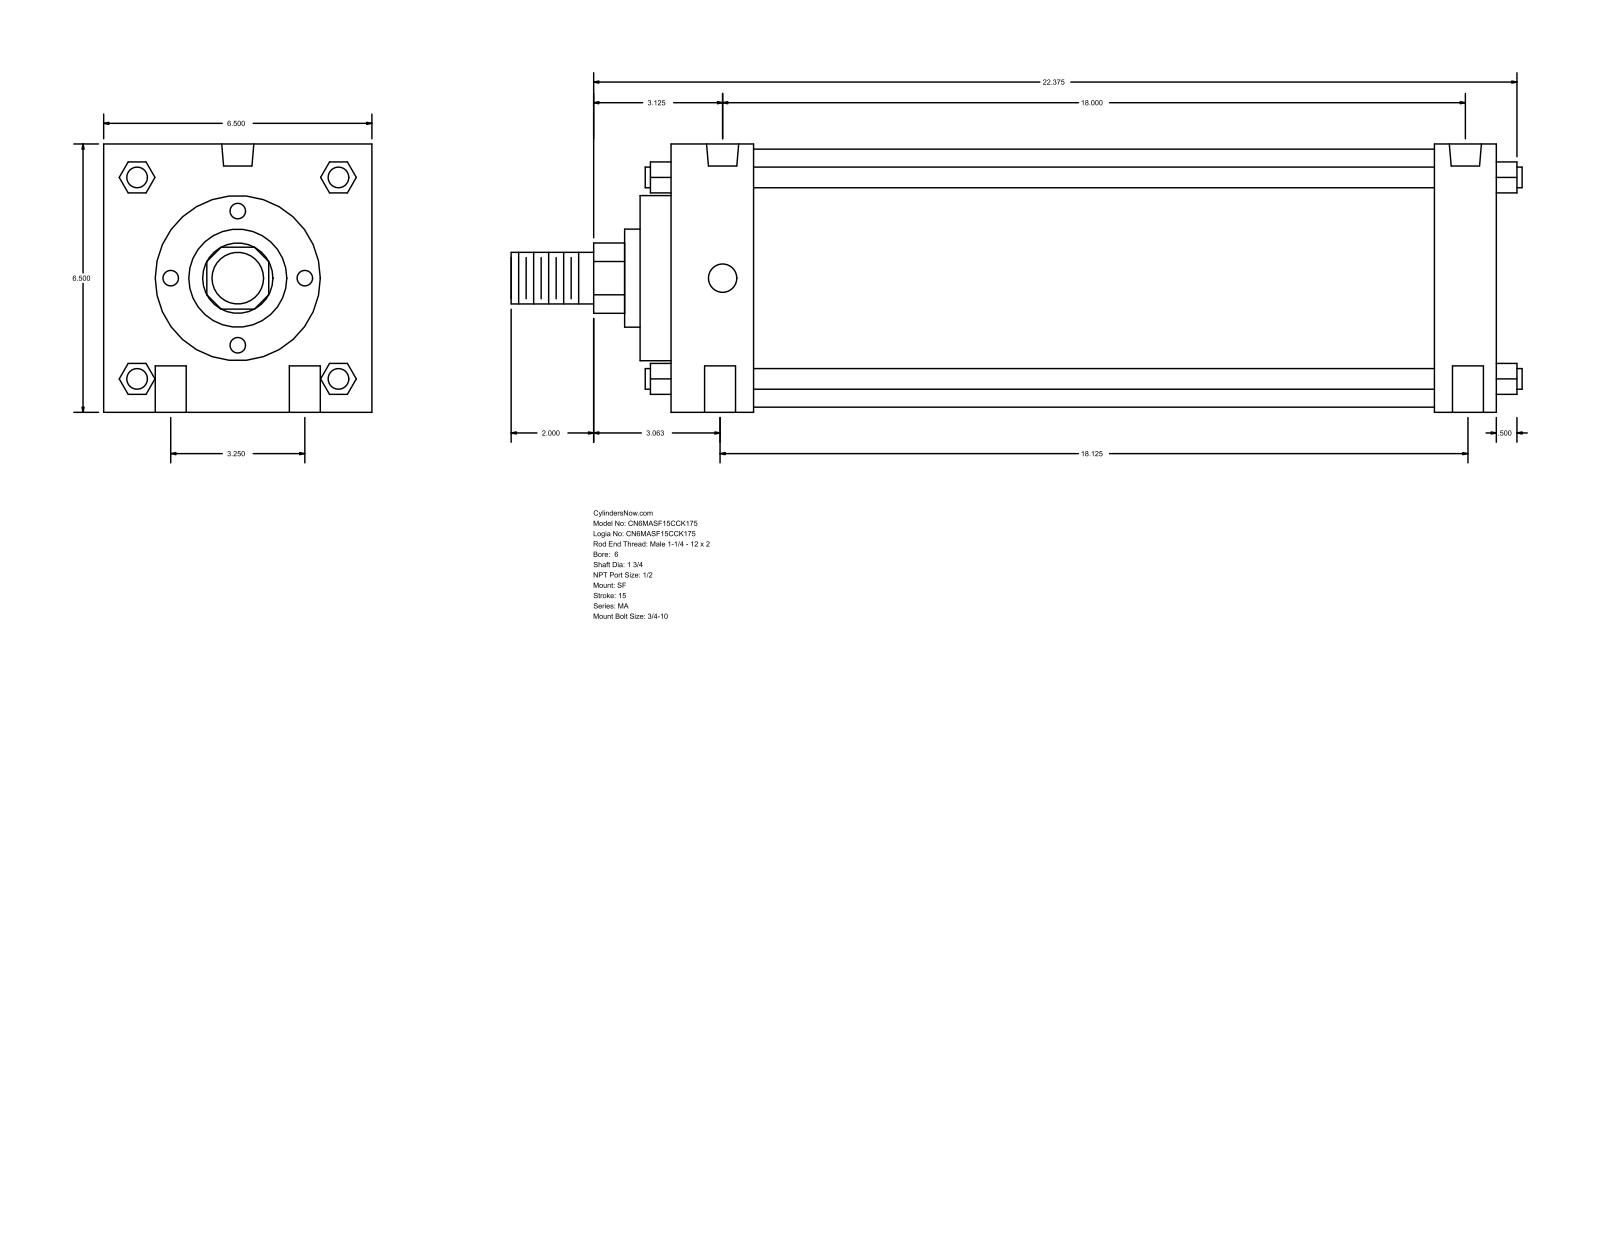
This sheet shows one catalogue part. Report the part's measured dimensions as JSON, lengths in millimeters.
{"part_name": "MA_SF__0600_1.75", "step_written_by": "GSSL Pune (CONFIG_CONTROL_DESIGN)", "units": "millimeters", "bodies": {"solids": 0, "faces": 126, "planar": 95, "cylindrical": 31, "other": 0}, "overall_size": [622.3, 165.1, 165.1], "round_holes": [[19.05, 4], [17.46, 2], [19.77, 2]], "round_bosses_or_shafts": [[12.7, 4], [158.75, 1], [101.6, 1], [60.33, 1], [44.45, 1], [31.75, 1]], "partial_cylinders_radius": [[21.63, 1]], "face_to_face_distances": [165.1, 508, 19.05, 50.8, 38.1, 469.9, 419.1, 457.2, 69.85, 488.95], "hole_center_spacings": [41.3, 82.54, 457.2, 460.37, 460.63, 460.64, 467.71]}
